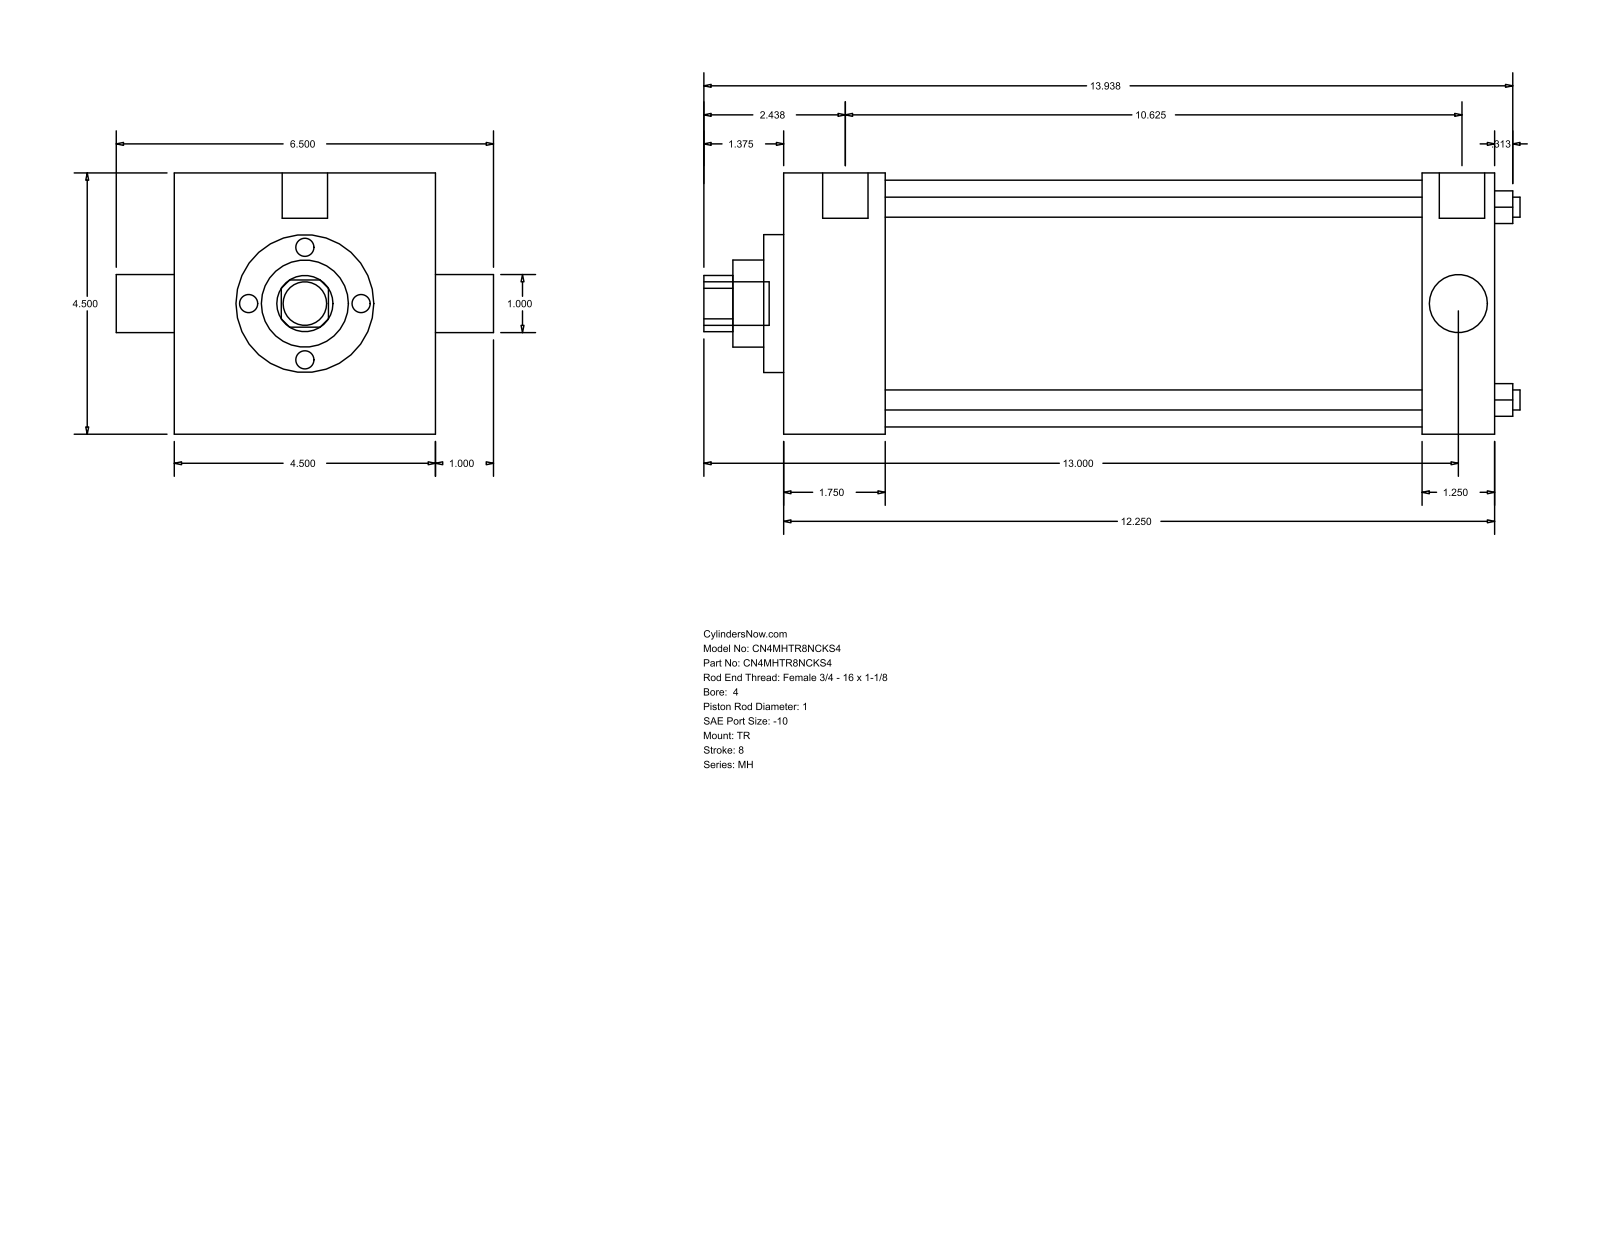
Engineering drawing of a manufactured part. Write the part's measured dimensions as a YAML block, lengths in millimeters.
part_name: "MH_TR__0400_1"
step_written_by: "GSSL Pune (CONFIG_CONTROL_DESIGN)"
units: millimeters
bodies: {solids: 0, faces: 86, planar: 61, cylindrical: 25, other: 0}
overall_size: [357.19, 165.1, 114.3]
round_holes:
  - {diameter: 8.76, count: 4}
  - {diameter: 25.4, count: 2}
  - {diameter: 38.1, count: 1}
  - {diameter: 60.33, count: 1}
  - {diameter: 107.95, count: 1}
round_bosses_or_shafts:
  - {diameter: 8.73, count: 3}
  - {diameter: 19.84, count: 2}
  - {diameter: 19.05, count: 1}
partial_cylinders:
  - {radius: 12.29, count: 1}
face_to_face_distances: [114.3, 311.15, 44.46, 266.69, 279.4, 234.94, 31.75, 8.73, 53.19, 288.13]
hole_center_spacings: [59.62, 84.32, 119.25]
